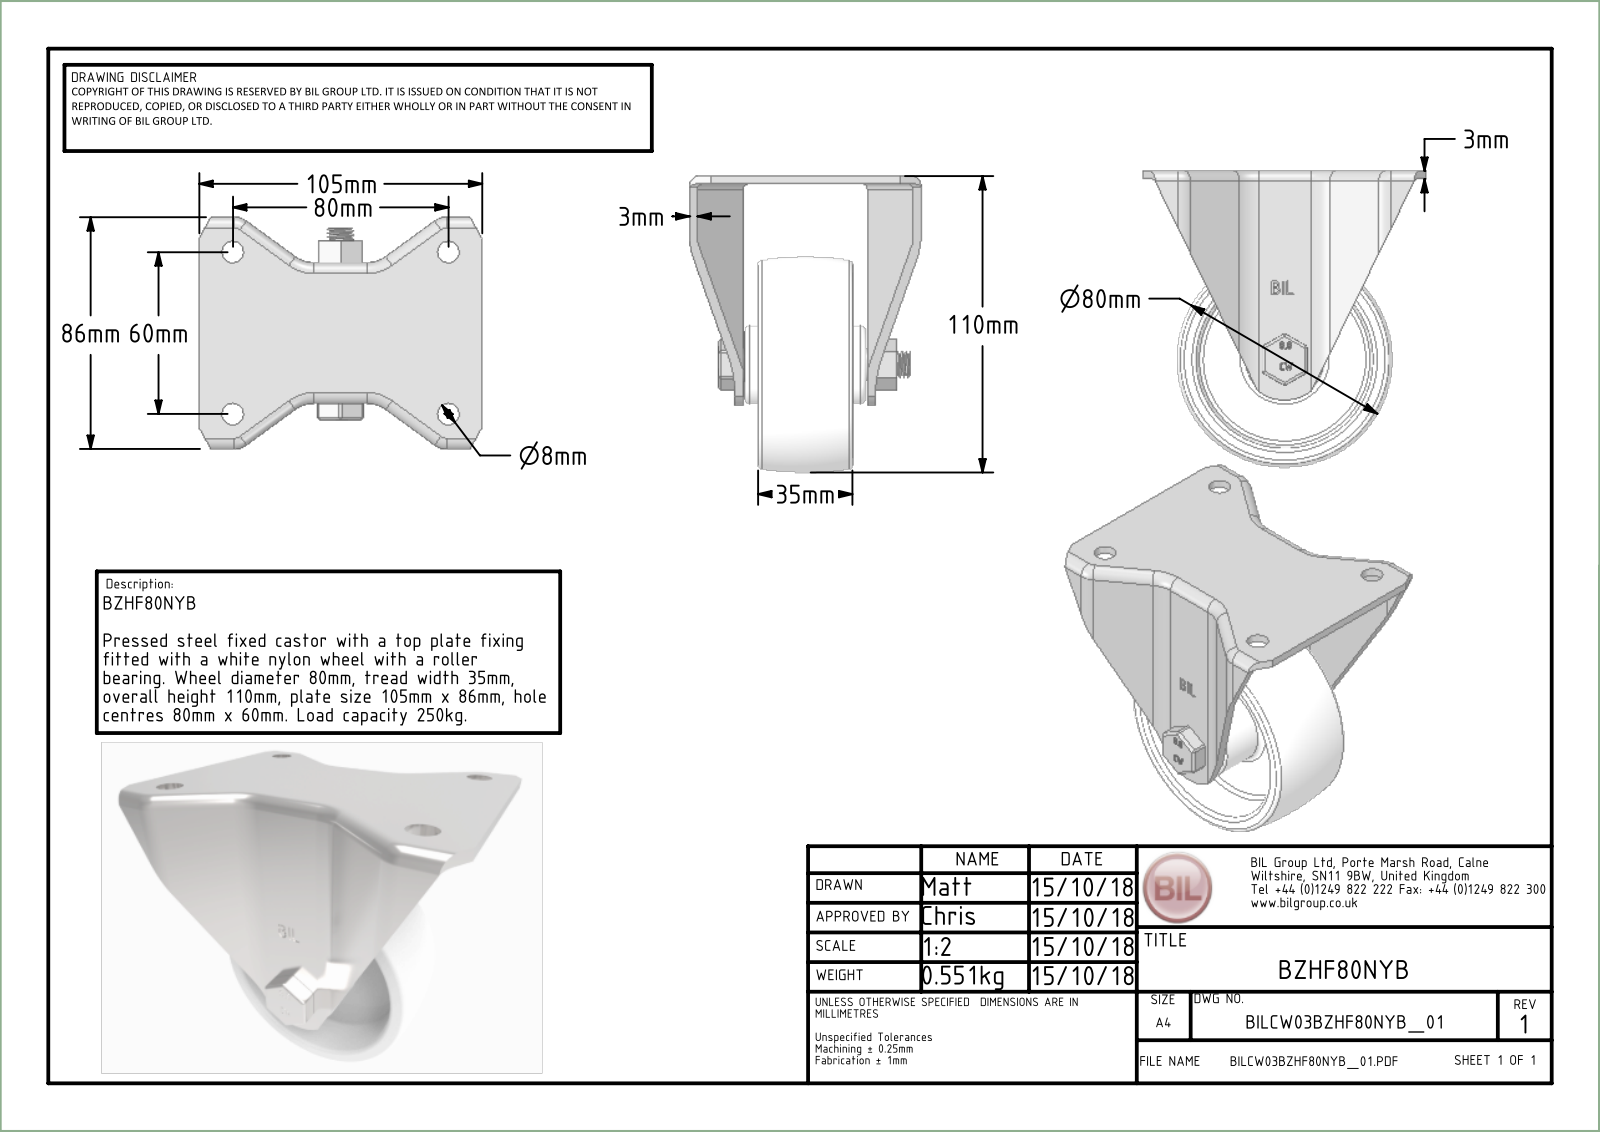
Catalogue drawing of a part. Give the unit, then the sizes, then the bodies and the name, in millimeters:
Units: millimetres
Overall size (bounding box): 110 × 105 × 87
Round holes (diameter × count): ⌀10 ×1, ⌀10.2 ×1, ⌀12 ×1, ⌀12.4 ×1, ⌀12.5 ×1, ⌀20 ×1
Round bosses / shafts (diameter × count): ⌀3.75 ×8, ⌀29 ×1, ⌀19.5 ×1, ⌀16 ×1, ⌀11.95 ×1, ⌀9.85 ×1, ⌀8.14 ×1
Partial cylindrical surfaces — rounded edges, fillets, slot ends (radius × count): R0.5 ×18, R3 ×12, R1.5 ×10, R10 ×9, R4.5 ×8, R0.75 ×6, R7 ×4, R13 ×4
Main face-to-face distances: 3, 26.5, 2, 45.5, 5.5, 51, 24.5, 53, 29.5, 23.5
Volume: 146 690 mm³ · Surface area: 82 481 mm²
Bodies: 16 solids, 493 faces (215 planar, 176 cylindrical, 102 other)
Part name (STEP PRODUCT): BZHF80NYB v3; BZHF80AS v1; BZHF80AS; ZINC PLATED, PRESSED STEEL BRACKET (+7 more)
STEP written by: Autodesk Translation Framework v14.4.0.0 (AUTOMOTIVE_DESIGN)
